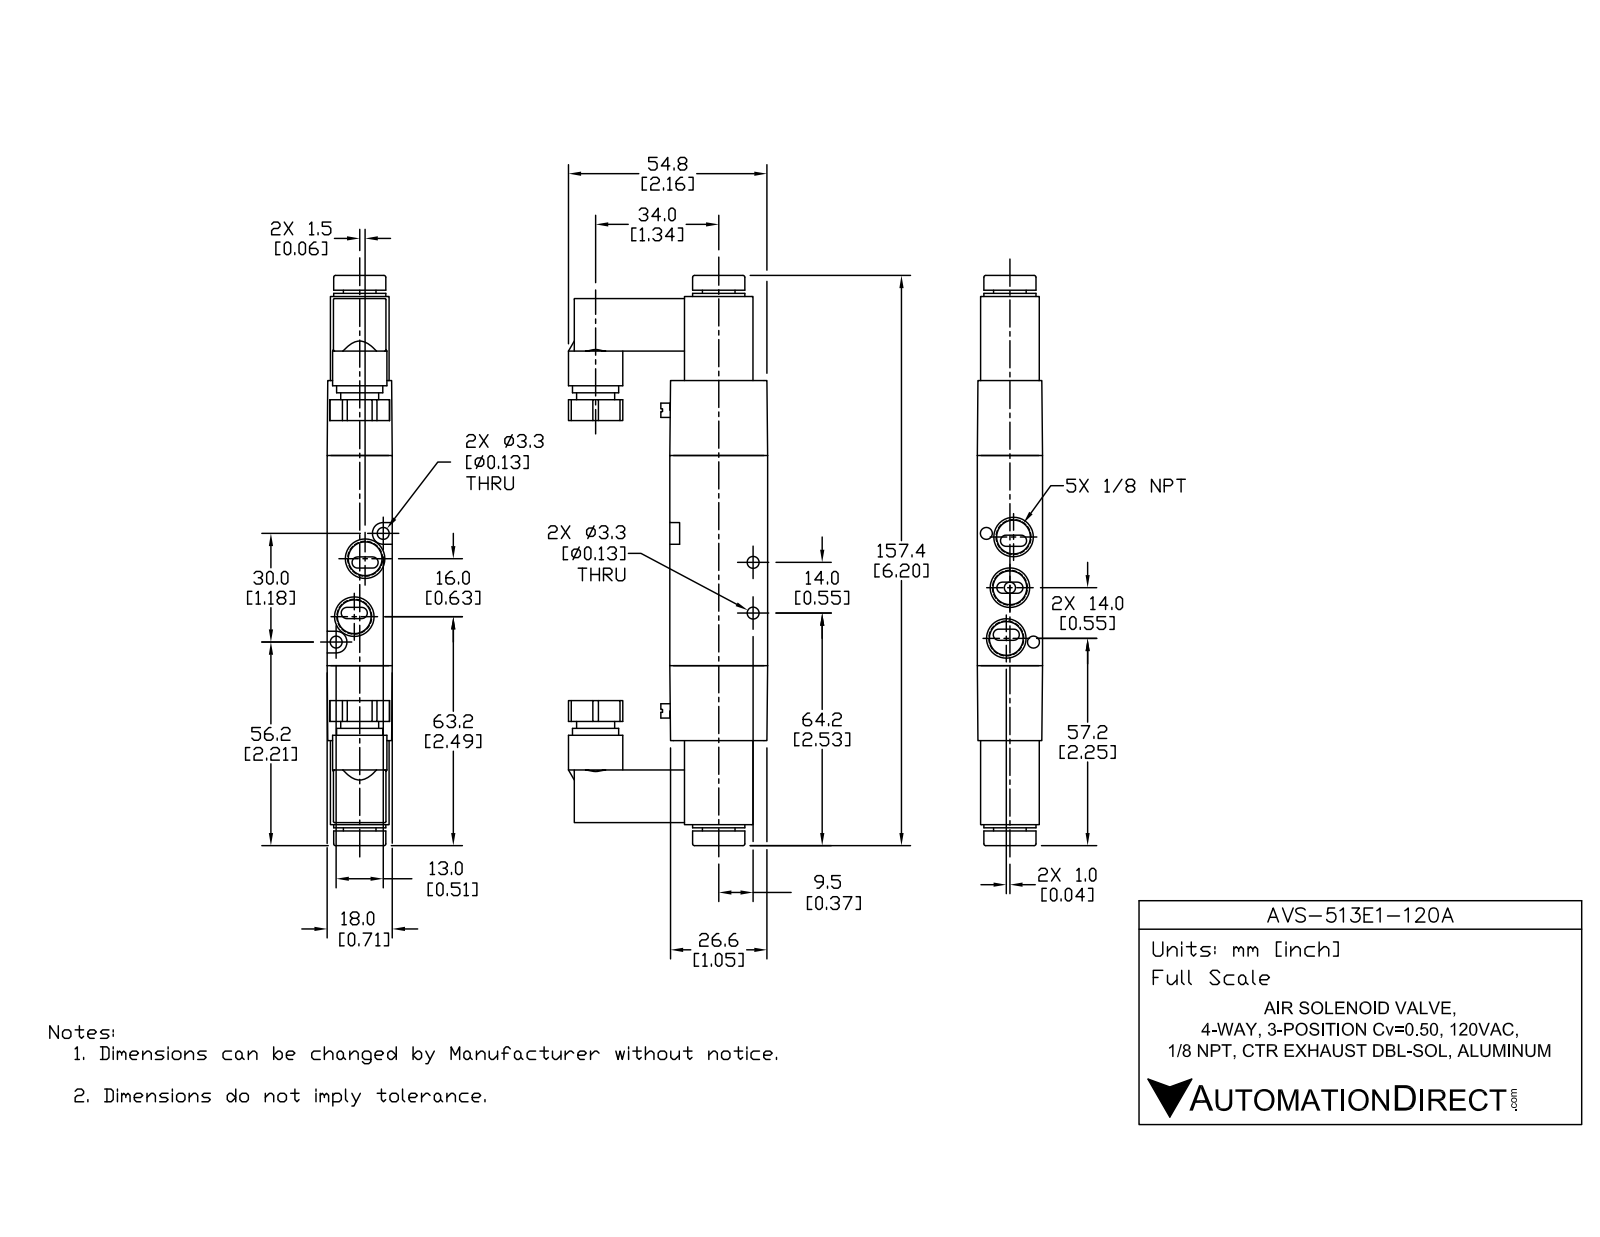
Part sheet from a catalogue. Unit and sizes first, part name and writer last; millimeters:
Units: millimetres
Overall size (bounding box): 157.4 × 55 × 18
Round holes (diameter × count): ⌀8.43 ×5, ⌀3.2 ×2, ⌀3.3 ×2, ⌀9.3 ×1
Round bosses / shafts (diameter × count): ⌀6.8 ×2, ⌀15 ×1, ⌀14.4 ×1, ⌀12.8 ×1, ⌀10.5 ×1, ⌀9 ×1
Partial cylindrical surfaces — rounded edges, fillets, slot ends (radius × count): R1.54 ×10, R0.3 ×8, R0.5 ×8, R1 ×8, R3 ×2
Main face-to-face distances: 1.75, 16.25, 18.21, 0.31, 14.5, 18, 23.66, 18.52, 58, 3.86
Hole centre spacings: 7.57, 14.04, 16.35, 29.52, 6.25, 6.82, 8.04, 8.19
Volume: 77 332 mm³ · Surface area: 24 997 mm²
Bodies: 5 solids, 246 faces (131 planar, 91 cylindrical, 24 other)
Part name (STEP PRODUCT): AVS-513E1-120A
STEP written by: SolidWorks 2021 (CONFIG_CONTROL_DESIGN)
